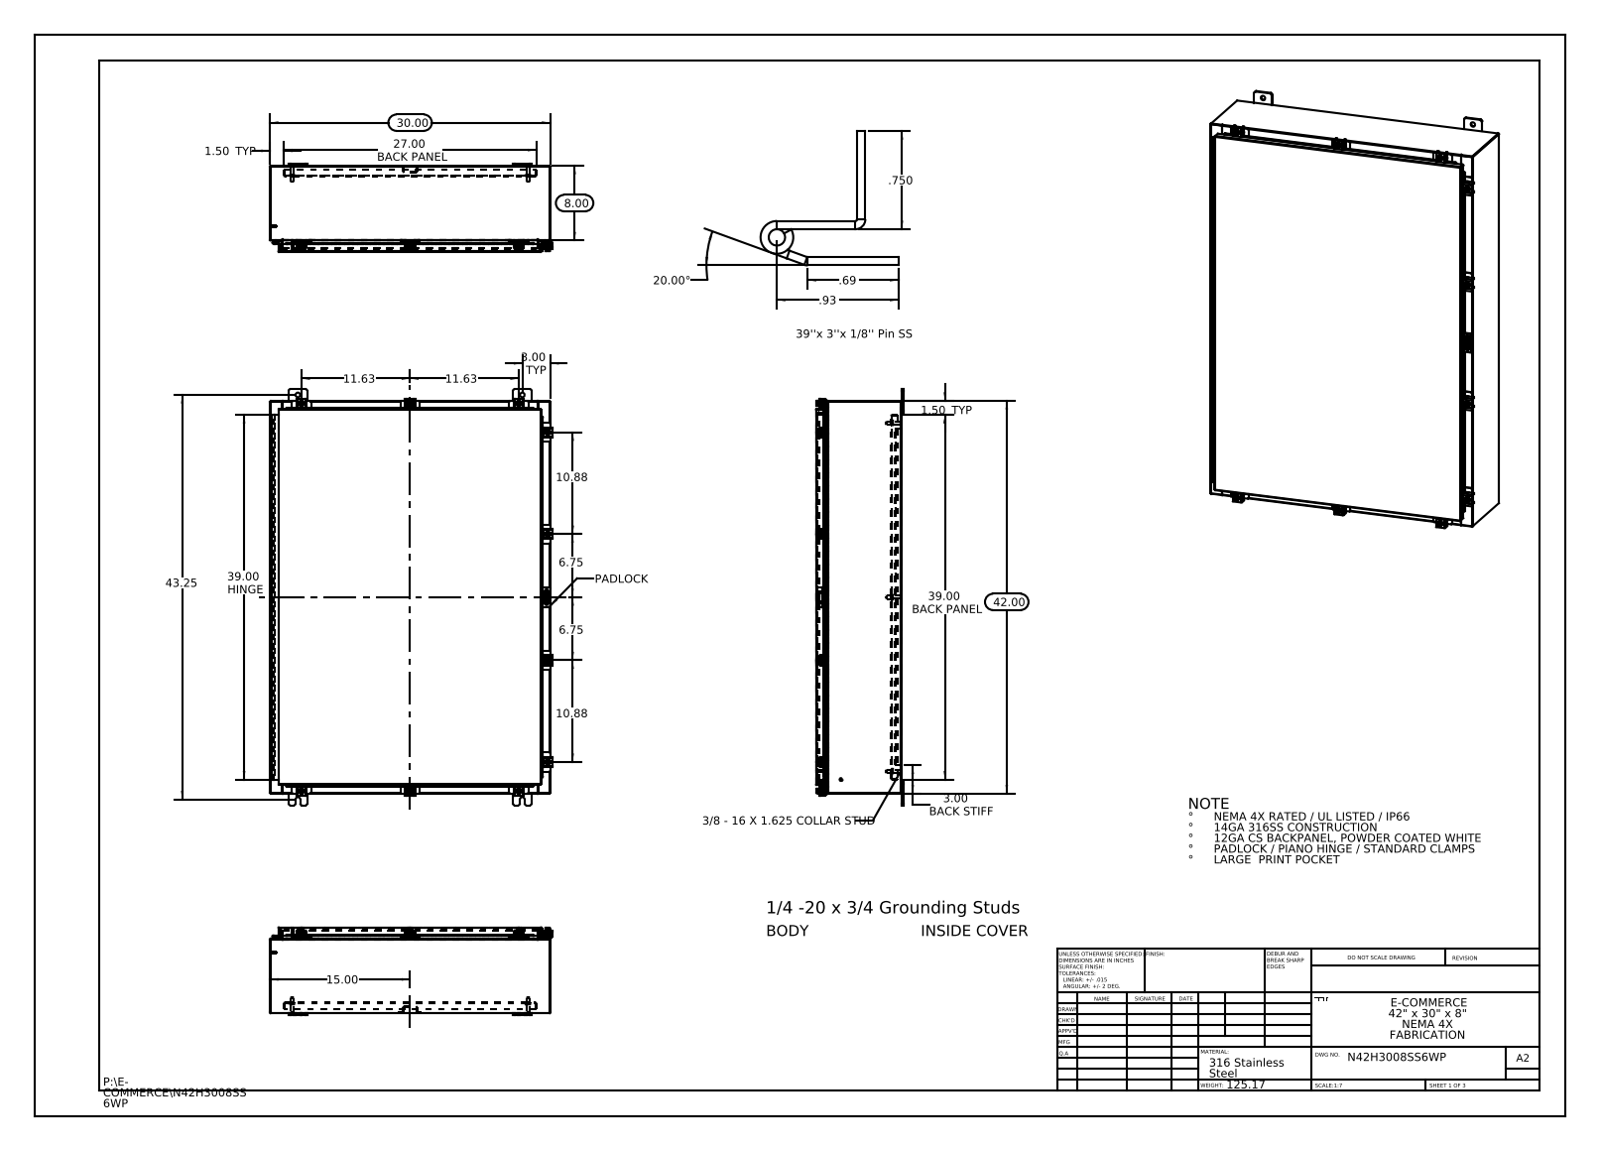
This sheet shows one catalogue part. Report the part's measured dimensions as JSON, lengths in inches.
{"part_name": "N42H3008SS6WP Bottom; N42H3008SS6WP Mounting Studs; N42H3008SS6WP Clamp Top; N42H3008SS6WP Backpanel (+8 more)", "step_written_by": "SolidWorks 2013 (CONFIG_CONTROL_DESIGN)", "units": "inches", "bodies": {"solids": 72, "faces": 2743, "planar": 1426, "cylindrical": 1157, "other": 160}, "overall_size": [44.5, 30.211, 9.389], "volume_in3": 439.2, "surface_area_in2": 10916, "round_holes": [[0.213, 10], [0.26, 10], [0.5, 10], [0.125, 2], [0.125, 1]], "round_bosses_or_shafts": [[0.25, 11], [0.5, 10], [0.399, 10], [0.625, 6], [0.375, 6], [0.33, 6], [0.315, 2], [0.236, 2]], "partial_cylinders_radius": [[0.06, 46], [0.013, 31], [0.088, 25], [0.19, 24], [0.12, 20], [0.141, 20], [0.05, 15], [0.08, 14]], "face_to_face_distances": [0.075, 9.126, 9.051, 0.104, 9.201, 1, 8.126, 1.075, 8.051, 1.179], "hole_center_spacings": [2.326, 18.625, 20.75, 24.268, 31.376, 39.363, 41.326, 43.05]}
